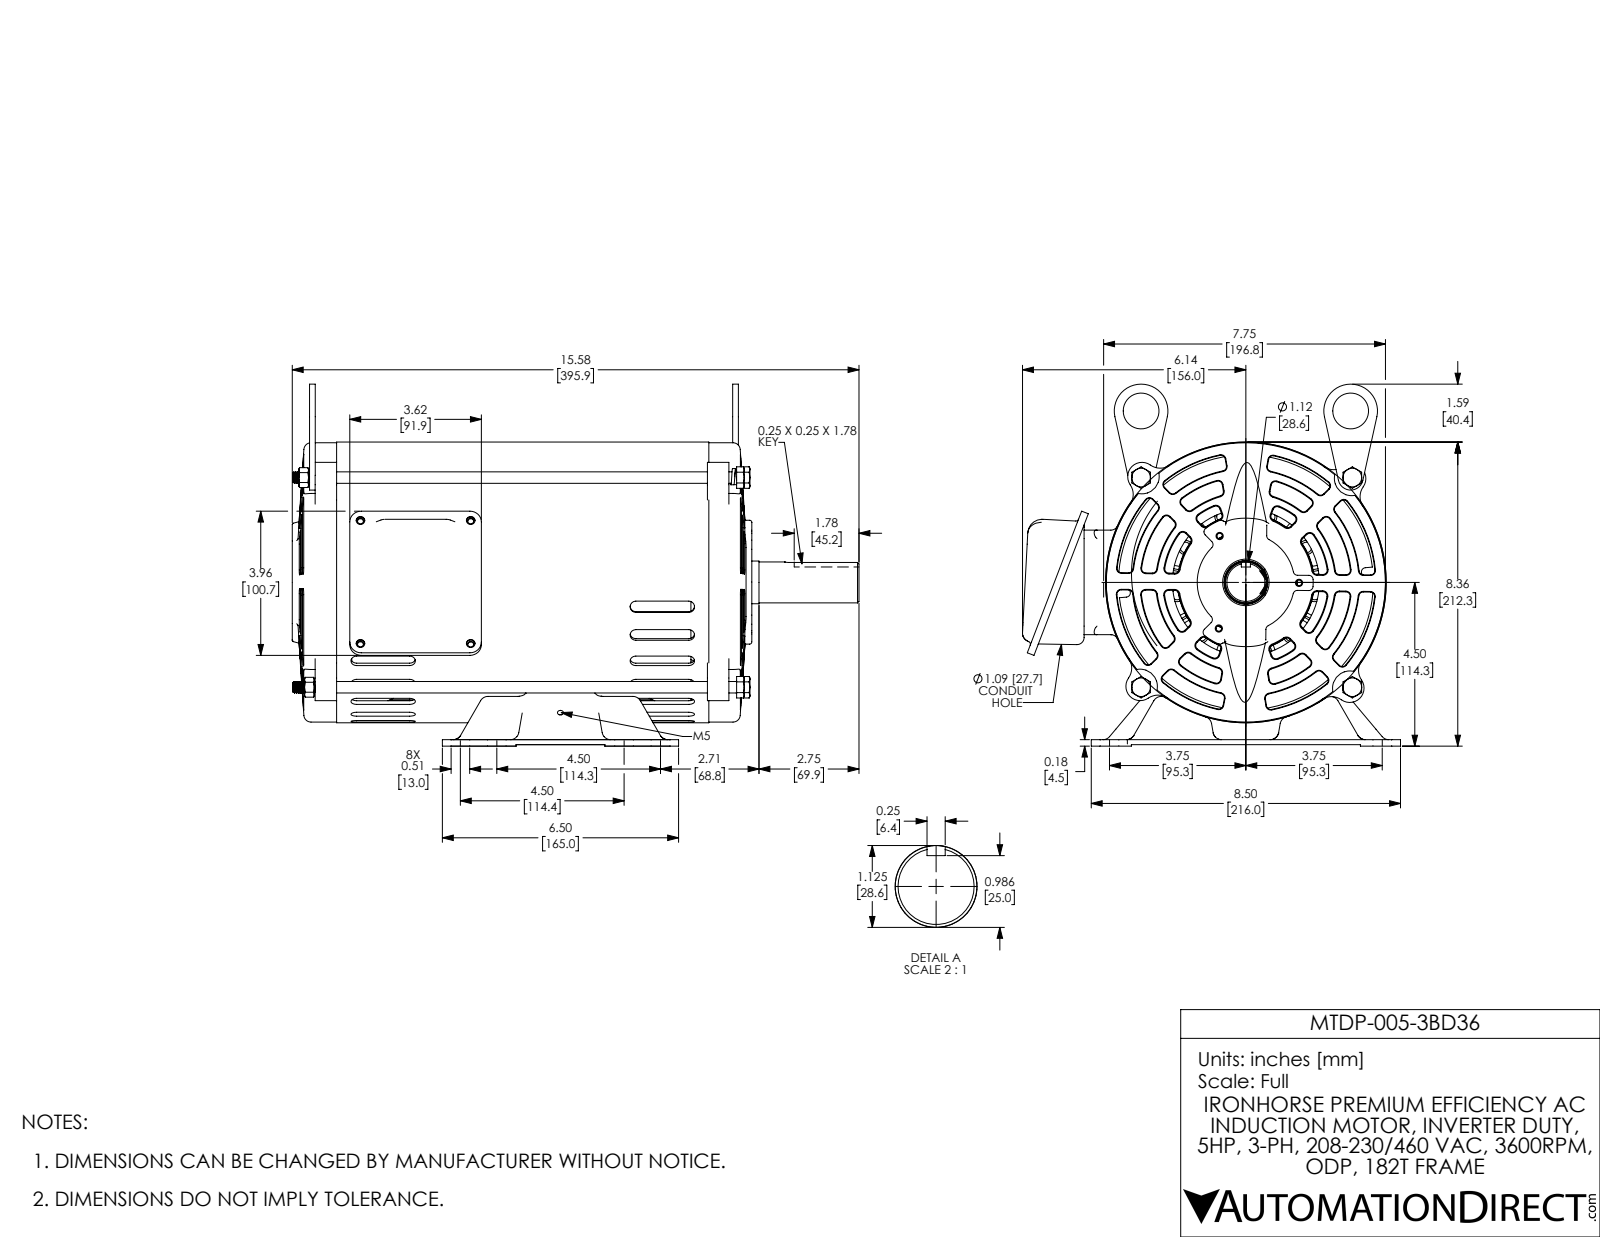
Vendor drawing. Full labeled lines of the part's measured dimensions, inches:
Part name (STEP PRODUCT): ODP-182_4_T EXT2 C 2 fXT Coord Red1
STEP written by: SolidWorks 2017 (AUTOMOTIVE_DESIGN)
Units: inches
Bodies: 26 solids, 3031 faces (723 planar, 1152 cylindrical, 1156 other)
Overall size (bounding box): 15.585 × 10.394 × 9.95
Volume: 394.6 in³ · Surface area: 1 889 in²
Round holes (diameter × count): ⌀0.165 ×9, ⌀0.236 ×8, ⌀0.512 ×8, ⌀0.368 ×4, ⌀0.394 ×4, ⌀0.15 ×3, ⌀0.28 ×3, ⌀0.984 ×3, ⌀0.276 ×2, ⌀1.181 ×2, ⌀0.866 ×1, ⌀1.201 ×1
Round bosses / shafts (diameter × count): ⌀0.315 ×4, ⌀0.262 ×4, ⌀0.445 ×3, ⌀7.008 ×2, ⌀7.677 ×1, ⌀4.701 ×1, ⌀1.575 ×1, ⌀1.496 ×1
Partial cylindrical surfaces — rounded edges, fillets, slot ends (radius × count): R0.157 ×59, R0.059 ×56, R0.236 ×45, R0.079 ×37, R0.118 ×33, R0.197 ×26, R0.039 ×20, R0.276 ×20
Main face-to-face distances: 0.039, 0.177, 0.138, 2.874, 8.189, 0.394, 5.315, 0.394, 5.709, 6.102
Hole centre spacings: 5.763, 2.91, 6.808, 3.031, 1, 1.969, 4.075, 4.5
